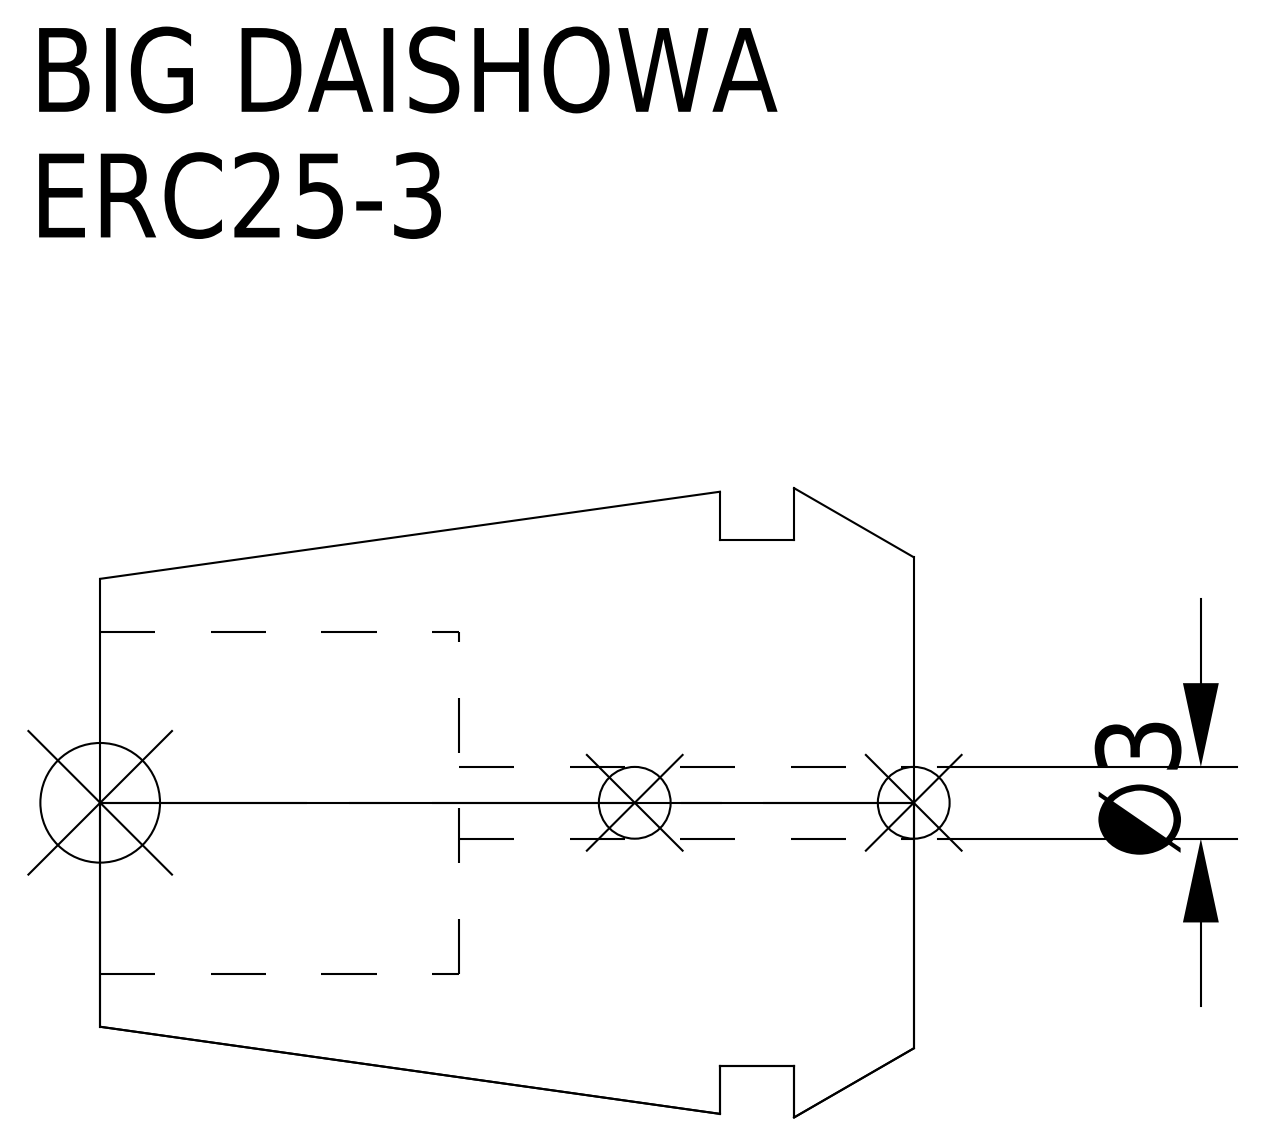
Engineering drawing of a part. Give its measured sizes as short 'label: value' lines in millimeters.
name: ERC25-3
written by: CREO PARAMETRIC BY PTC INC, 2016380 (AUTOMOTIVE_DESIGN)
unit: mm
bodies: 1 solid, 15 faces (5 planar, 6 cylindrical, 4 other)
size: 34 × 26.3 × 26.3
volume: 11 059 mm³; area: 4 235 mm²
holes: 1× ⌀3, 1× ⌀14.3
bosses: 1× ⌀22
face distances: 5, 19, 14, 8.1, 3.1, 10.9, 34, 29, 25.9, 15
